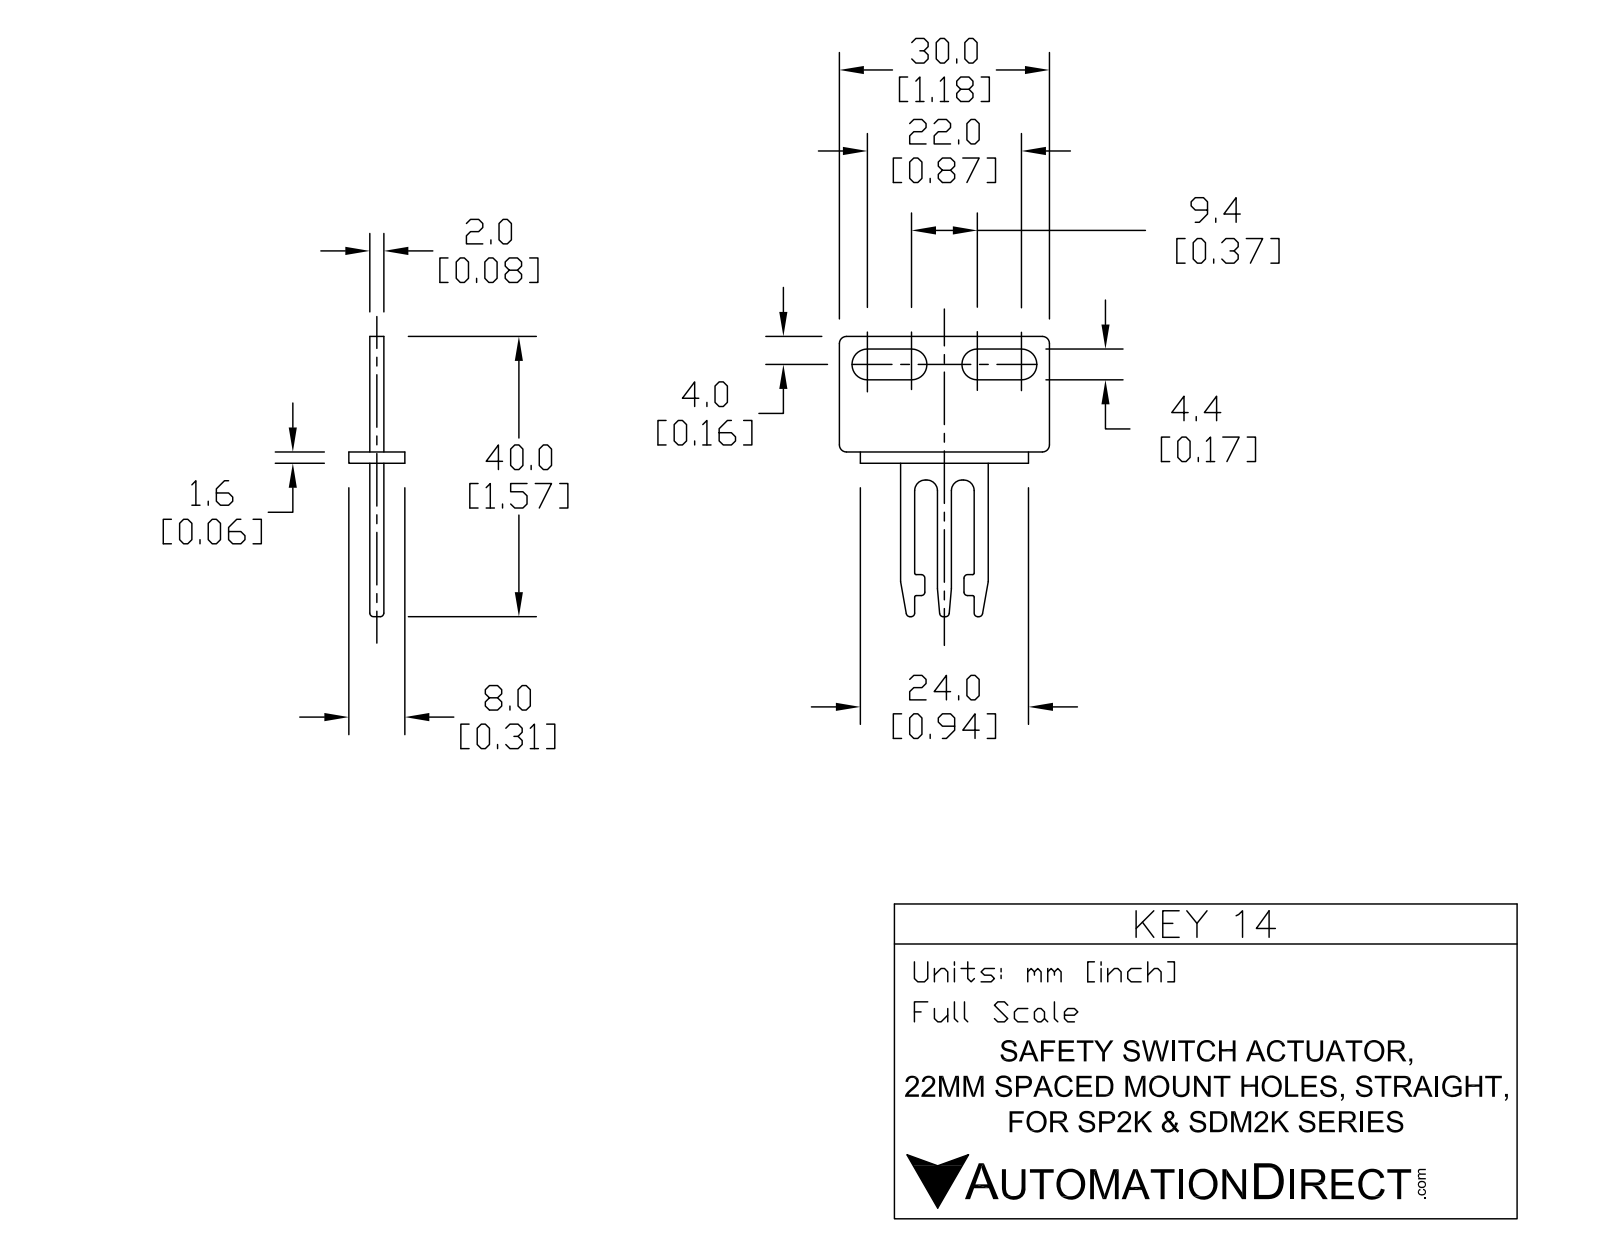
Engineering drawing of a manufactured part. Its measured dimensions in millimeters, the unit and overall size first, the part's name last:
Units: millimetres
Overall size (bounding box): 40 × 30 × 8
Partial cylindrical surfaces — rounded edges, fillets, slot ends (radius × count): R0.5 ×42, R1 ×8, R0.2 ×4, R1.5 ×4, R2.2 ×4
Main face-to-face distances: 2, 1.6, 3, 5, 5.3, 16.5, 18.1, 8.7, 21.3, 2.1
Volume: 1 400 mm³ · Surface area: 2 121 mm²
Bodies: 2 solids, 160 faces (56 planar, 76 cylindrical, 28 other)
Part name (STEP PRODUCT): KEY14
STEP written by: SolidWorks 2019 (CONFIG_CONTROL_DESIGN)
